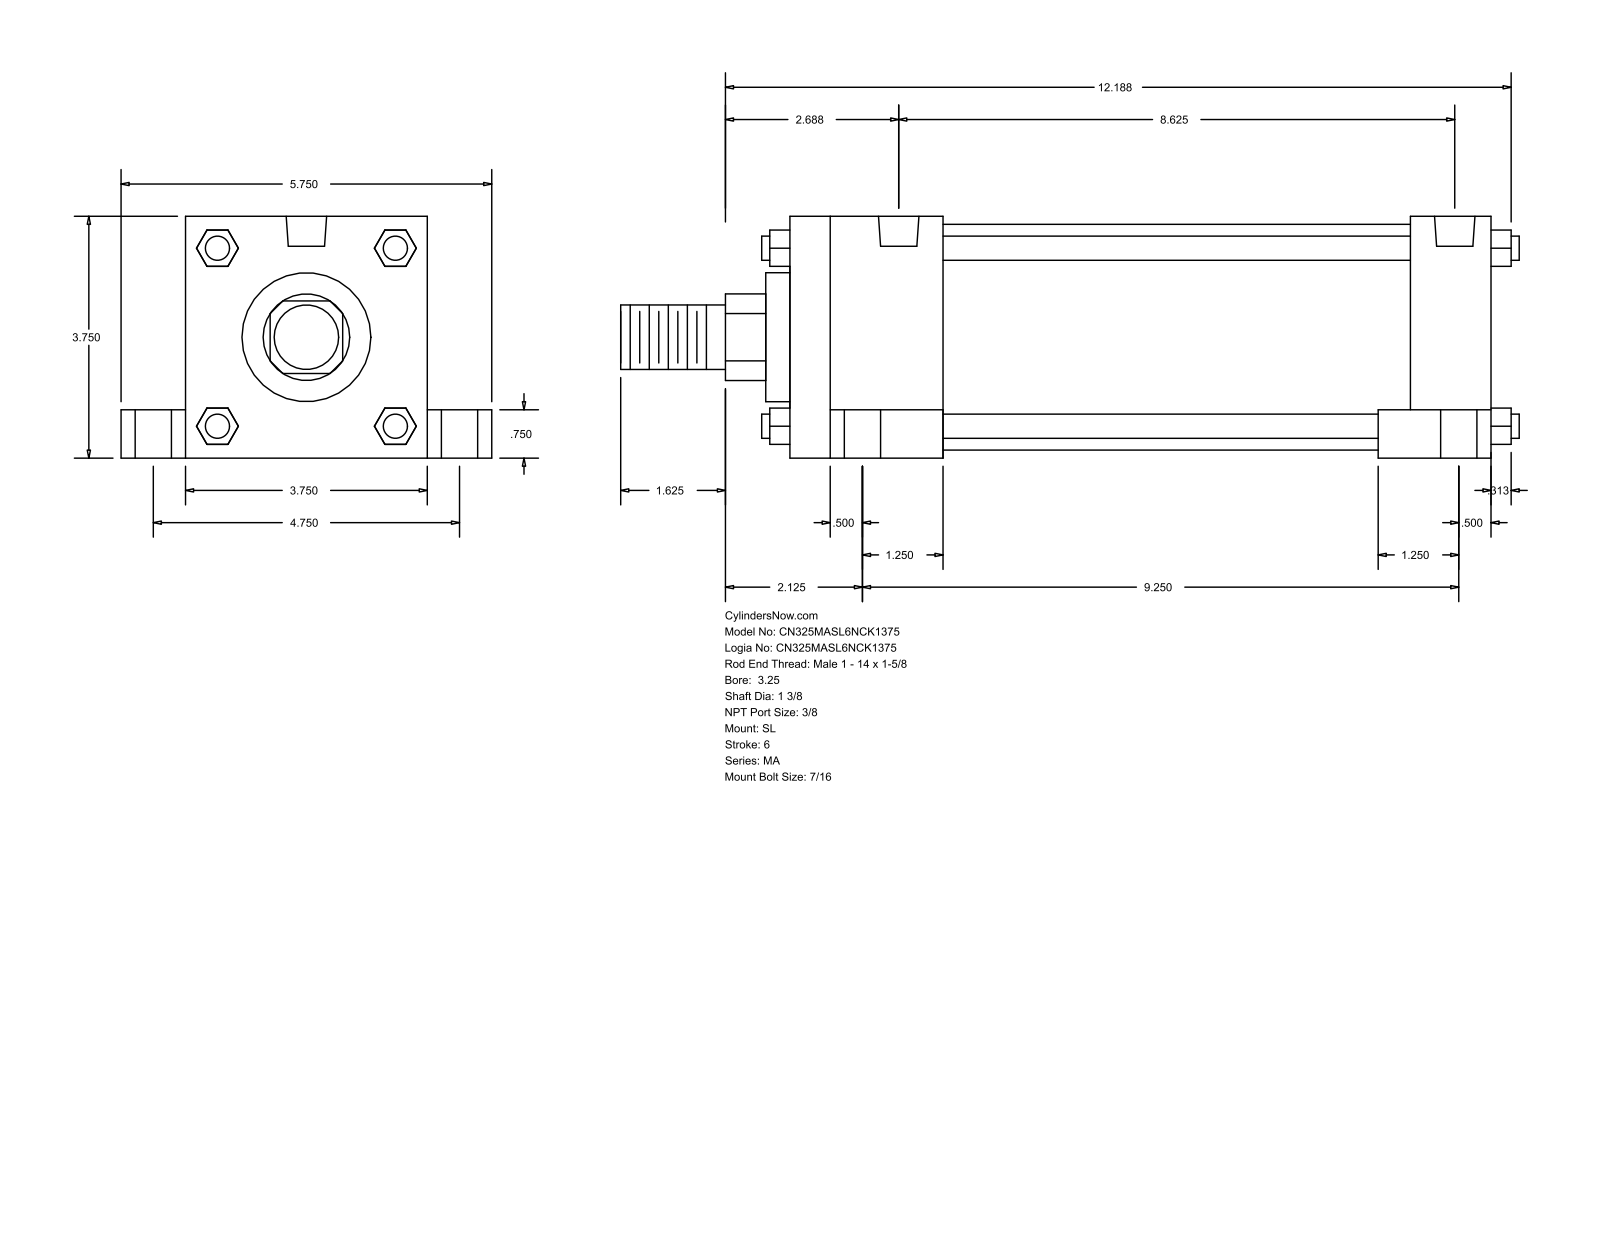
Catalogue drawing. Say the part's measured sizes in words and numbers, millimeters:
The part is named "MA_SL__0325_1.375". Its 3-D file was written by "GSSL Pune (CONFIG_CONTROL_DESIGN)". It is 0 solids with 148 faces: 112 planar, 36 cylindrical and 0 other. Overall it measures 354.01 by 146.05 by 95.25 millimeters. Round holes: 4 of diameter 11.11, 4 of diameter 14.29, 4 of diameter 20.64, 2 of diameter 15.93. Round bosses or shafts: 4 of diameter 9.53, 1 of diameter 88.9, 1 of diameter 50.8, 1 of diameter 34.92, 1 of diameter 25.4. Partial cylindrical surfaces (rounded edges, fillets, slot ends): 1 of radius 17.06. The main face-to-face distances are 95.24, 276.22, 25.41, 120.65, 244.48, 31.74, 60.32, 184.16, 215.9, 19.05. The hole center spacings are 4.77, 60.35, 60.66, 62, 63.27, 120.66, 209.54, 214.31.
